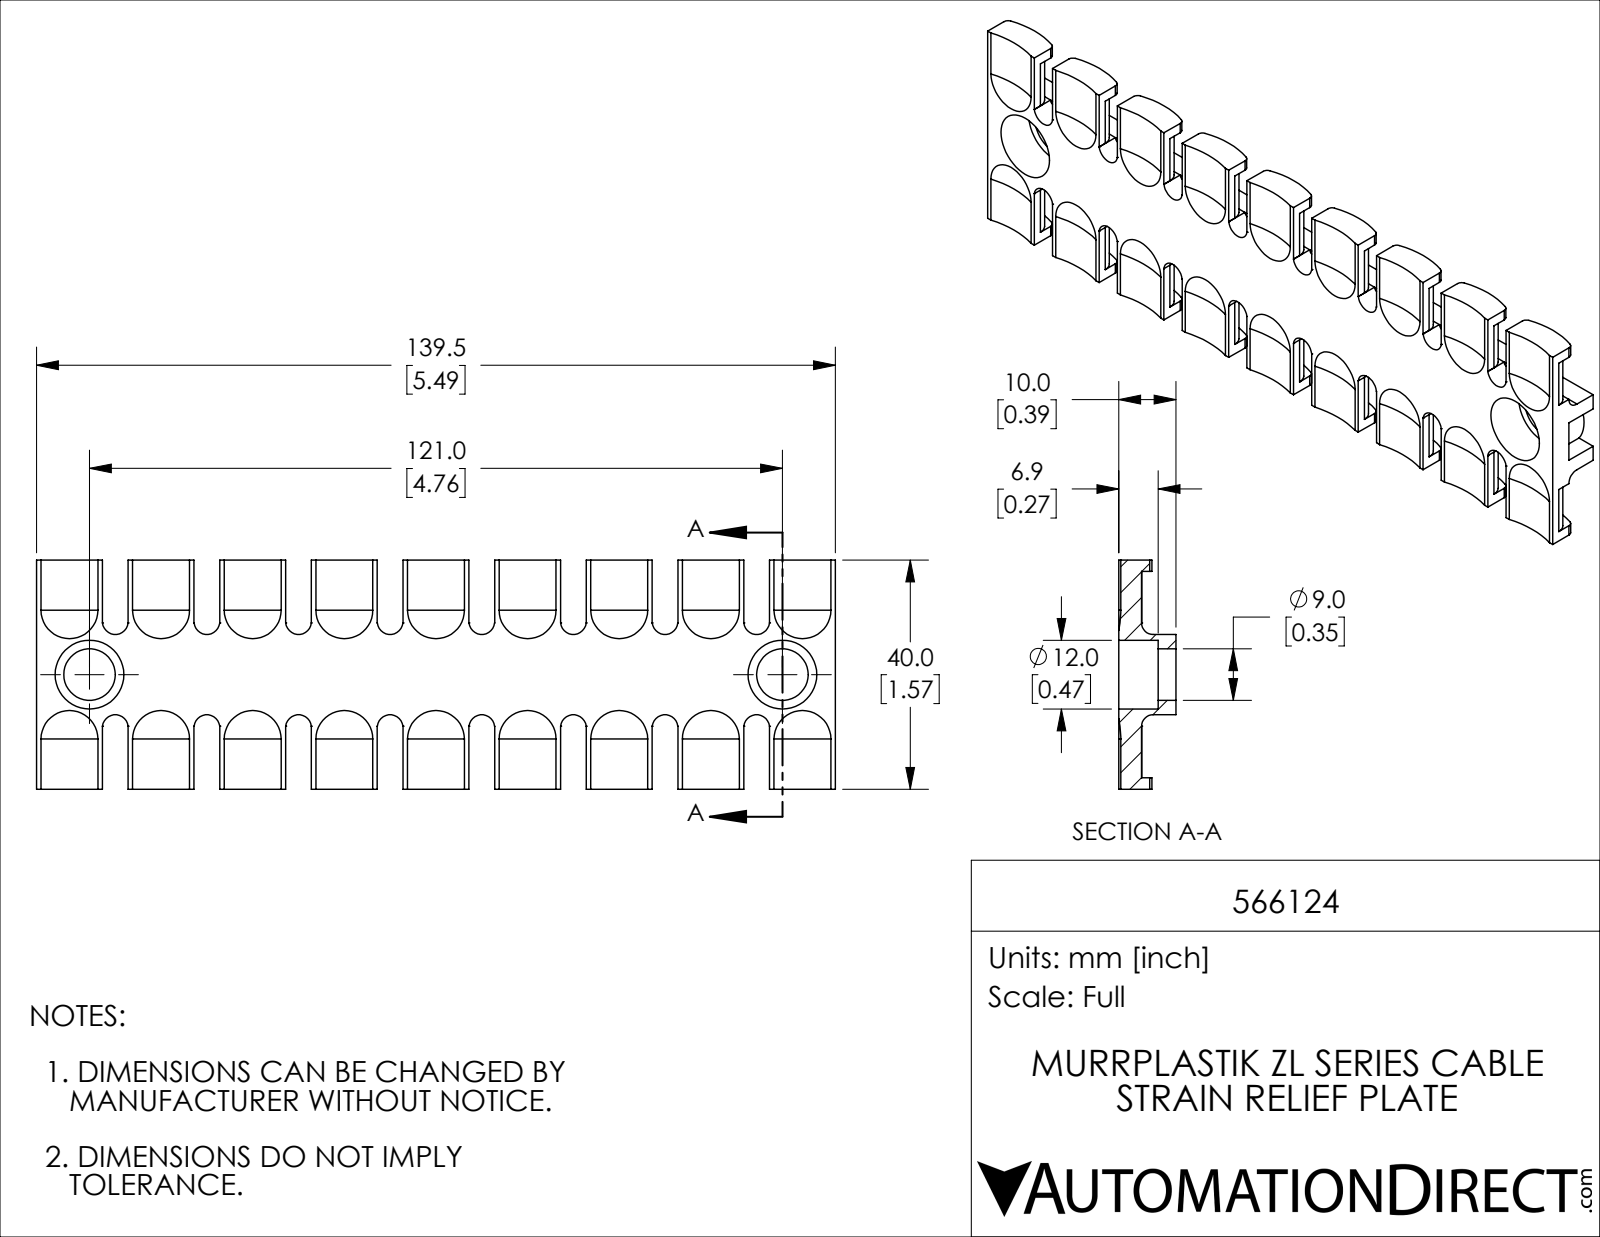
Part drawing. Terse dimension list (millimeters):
name: 566124
written by: SolidWorks 2019 (CONFIG_CONTROL_DESIGN)
unit: mm
bodies: 1 solid, 355 faces (154 planar, 183 cylindrical, 18 other)
size: 139.5 × 40 × 10
volume: 22 721 mm³; area: 16 495 mm²
holes: 2× ⌀9, 2× ⌀12
rounds: 18× R1, 18× R2.5, 16× R2.25, 9× R16, 9× R18, 2× R2, 2× R7
face distances: 4, 11, 16, 27, 3, 13, 24, 6, 10, 14
hole spacings: 121
